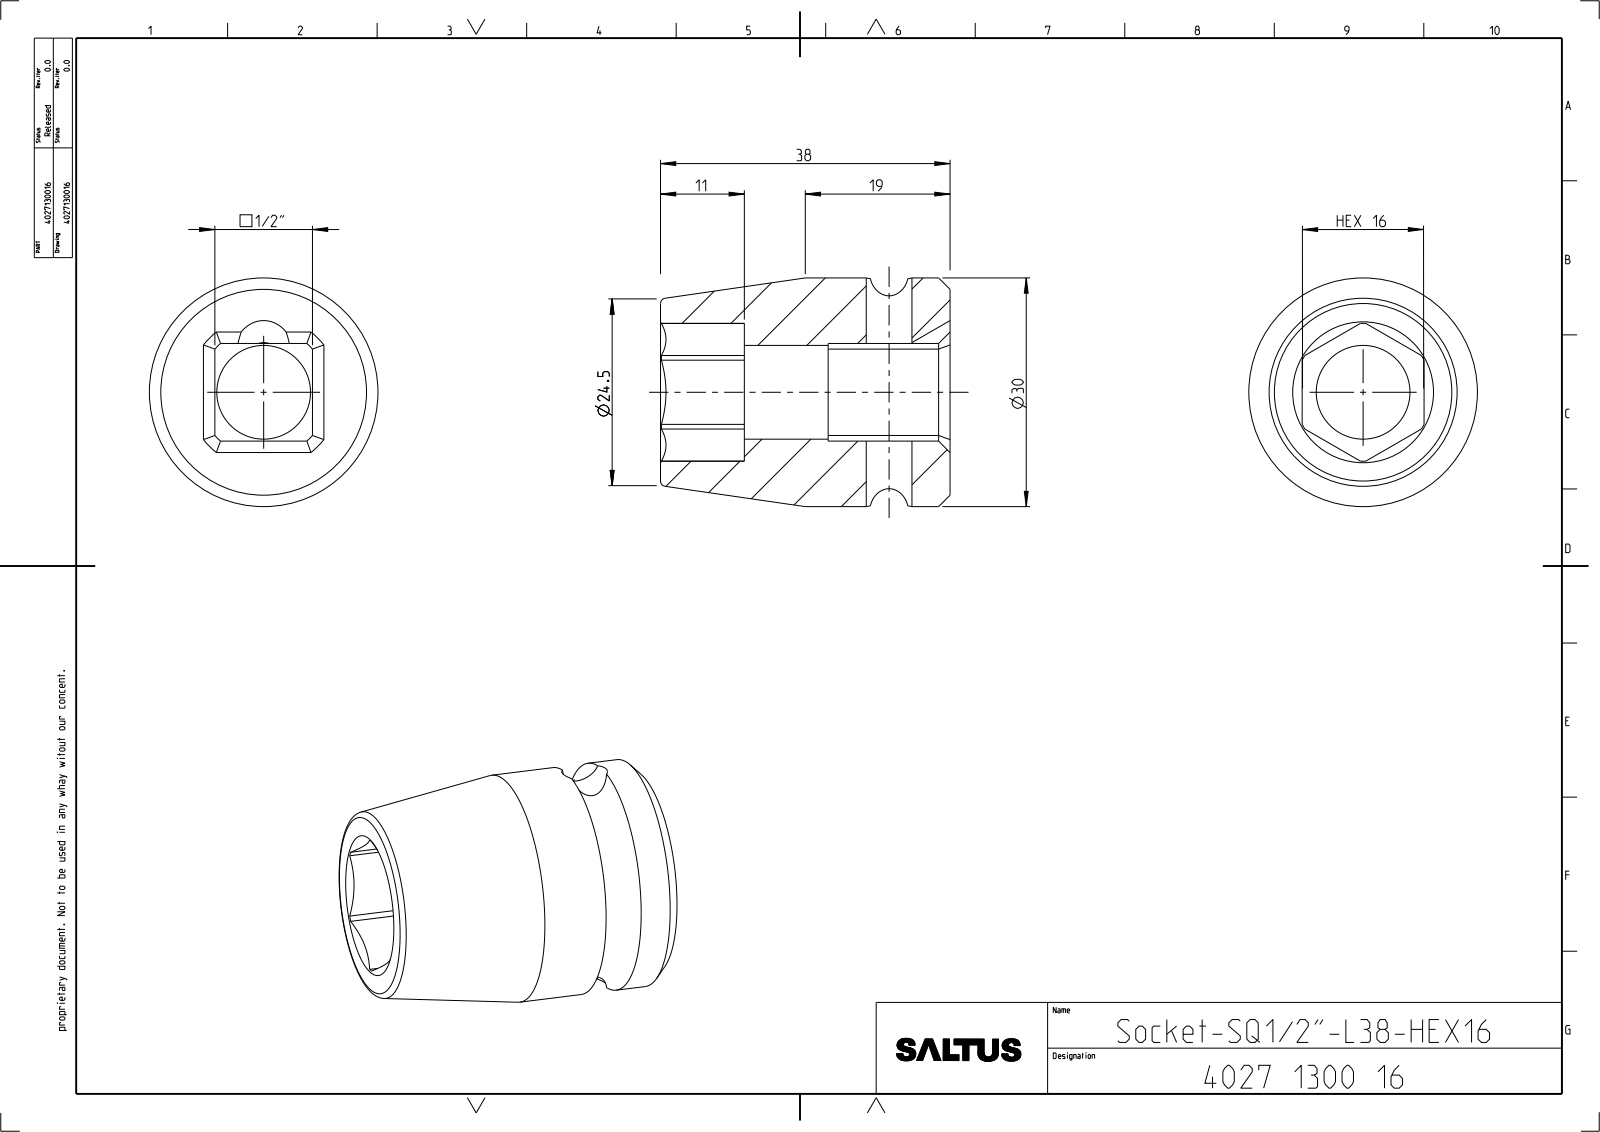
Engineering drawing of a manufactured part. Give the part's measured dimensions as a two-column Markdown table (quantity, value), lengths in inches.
| quantity | value |
| --- | --- |
| part name | 4027130016 |
| STEP written by | CREO PARAMETRIC BY PTC INC, 2022414 (CONFIG_CONTROL_DESIGN) |
| units | inches |
| bodies | 1 solid, 54 faces (19 planar, 21 cylindrical, 14 other) |
| overall size | 1.496 × 1.181 × 1.181 |
| volume | 1.034 in³ |
| surface area | 9.787 in² |
| round holes (diameter × count) | 0.236 × 1, 0.484 × 1 |
| round bosses / shafts (diameter × count) | 1.181 × 1 |
| partial cylindrical surfaces (radius × count) | 0.157 × 1, 0.337 × 1, 0.356 × 1 |
| main face-to-face distances | 0.63, 0.505, 0.063, 0.567, 1.496, 0.433, 1.063, 0.866 |
